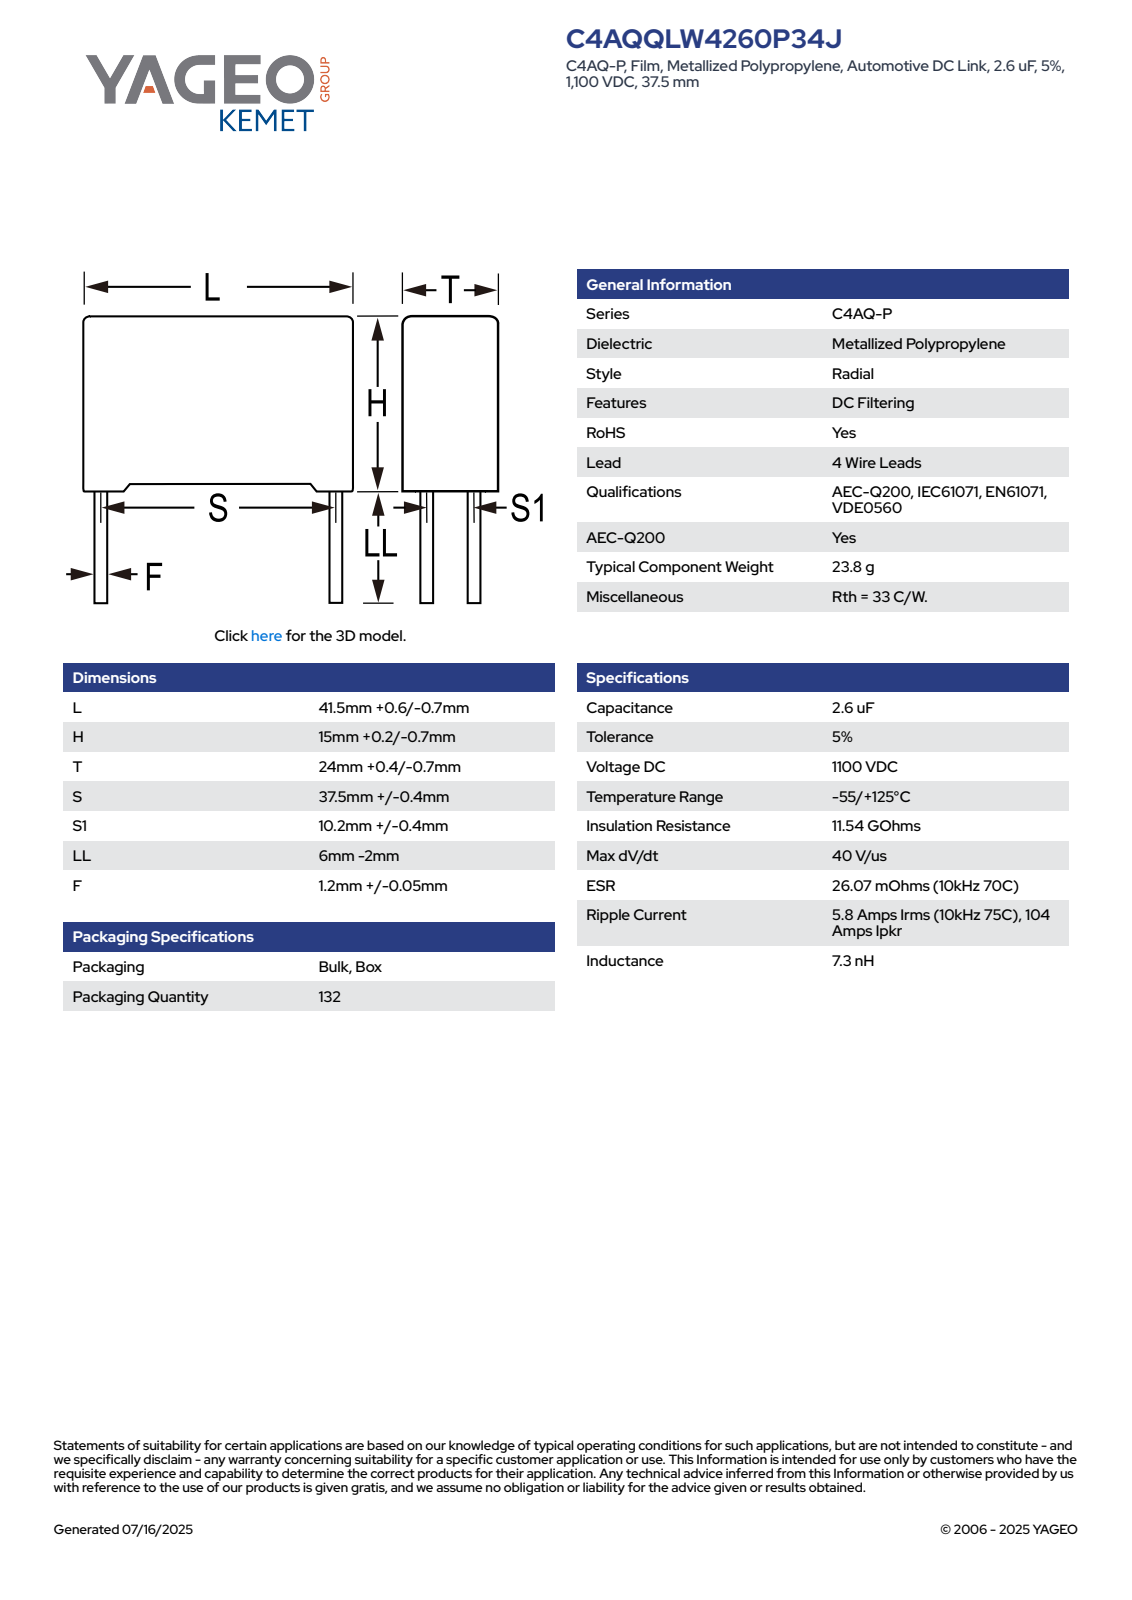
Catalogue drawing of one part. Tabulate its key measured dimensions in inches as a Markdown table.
| quantity | value |
| --- | --- |
| part name | CFP_RB4_41.5X15X24_L42.1H15.2T24.4S37.5S110.2LL4F1.25 |
| STEP written by | SolidWorks 2014 (AUTOMOTIVE_DESIGN) |
| units | inches |
| bodies | 4 solids, 87 faces (79 planar, 8 cylindrical, 0 other) |
| overall size | 1.657 × 0.961 × 0.756 |
| volume | 0.929 in³ |
| surface area | 6.612 in² |
| round bosses / shafts (diameter × count) | 0.049 × 4 |
| main face-to-face distances | 0.581, 0.961, 1.657, 0.018, 0.598, 0.961, 0.059, 1.598, 0.902, 1.539 |
